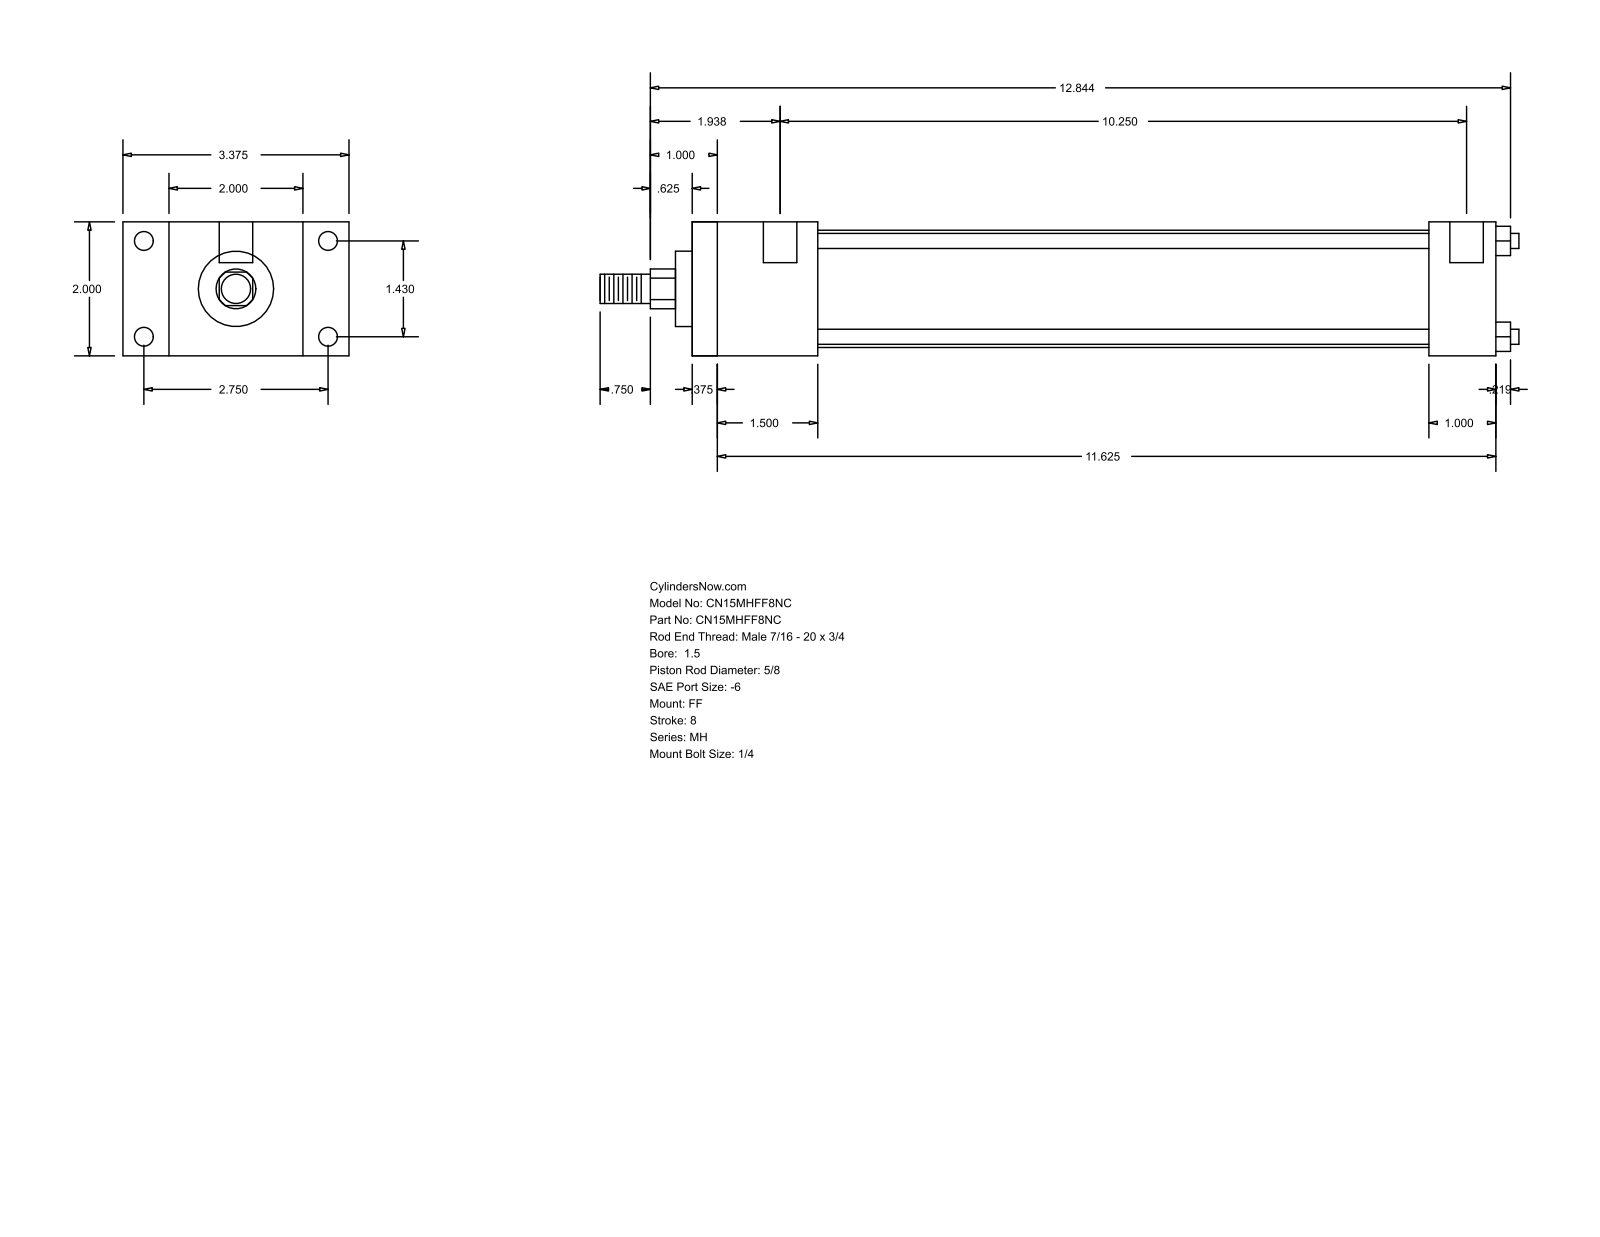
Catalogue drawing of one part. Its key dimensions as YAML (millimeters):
part_name: "MH_FF__0150_0.625"
step_written_by: "GSSL Pune (CONFIG_CONTROL_DESIGN)"
units: millimeters
bodies: {solids: 0, faces: 92, planar: 64, cylindrical: 28, other: 0}
overall_size: [348.46, 85.72, 50.8]
round_holes:
  - {diameter: 5.56, count: 4}
  - {diameter: 7.14, count: 4}
  - {diameter: 12.7, count: 2}
round_bosses_or_shafts:
  - {diameter: 5.71, count: 4}
  - {diameter: 44.45, count: 1}
  - {diameter: 28.57, count: 1}
  - {diameter: 15.88, count: 1}
  - {diameter: 11.11, count: 1}
partial_cylinders:
  - {radius: 7.54, count: 1}
face_to_face_distances: [50.8, 304.8, 9.52, 295.28, 17.46, 68.26, 47.62, 38.1, 257.18, 279.39]
hole_center_spacings: [36.32, 69.84, 78.72, 263.52, 3.17, 260.35]
